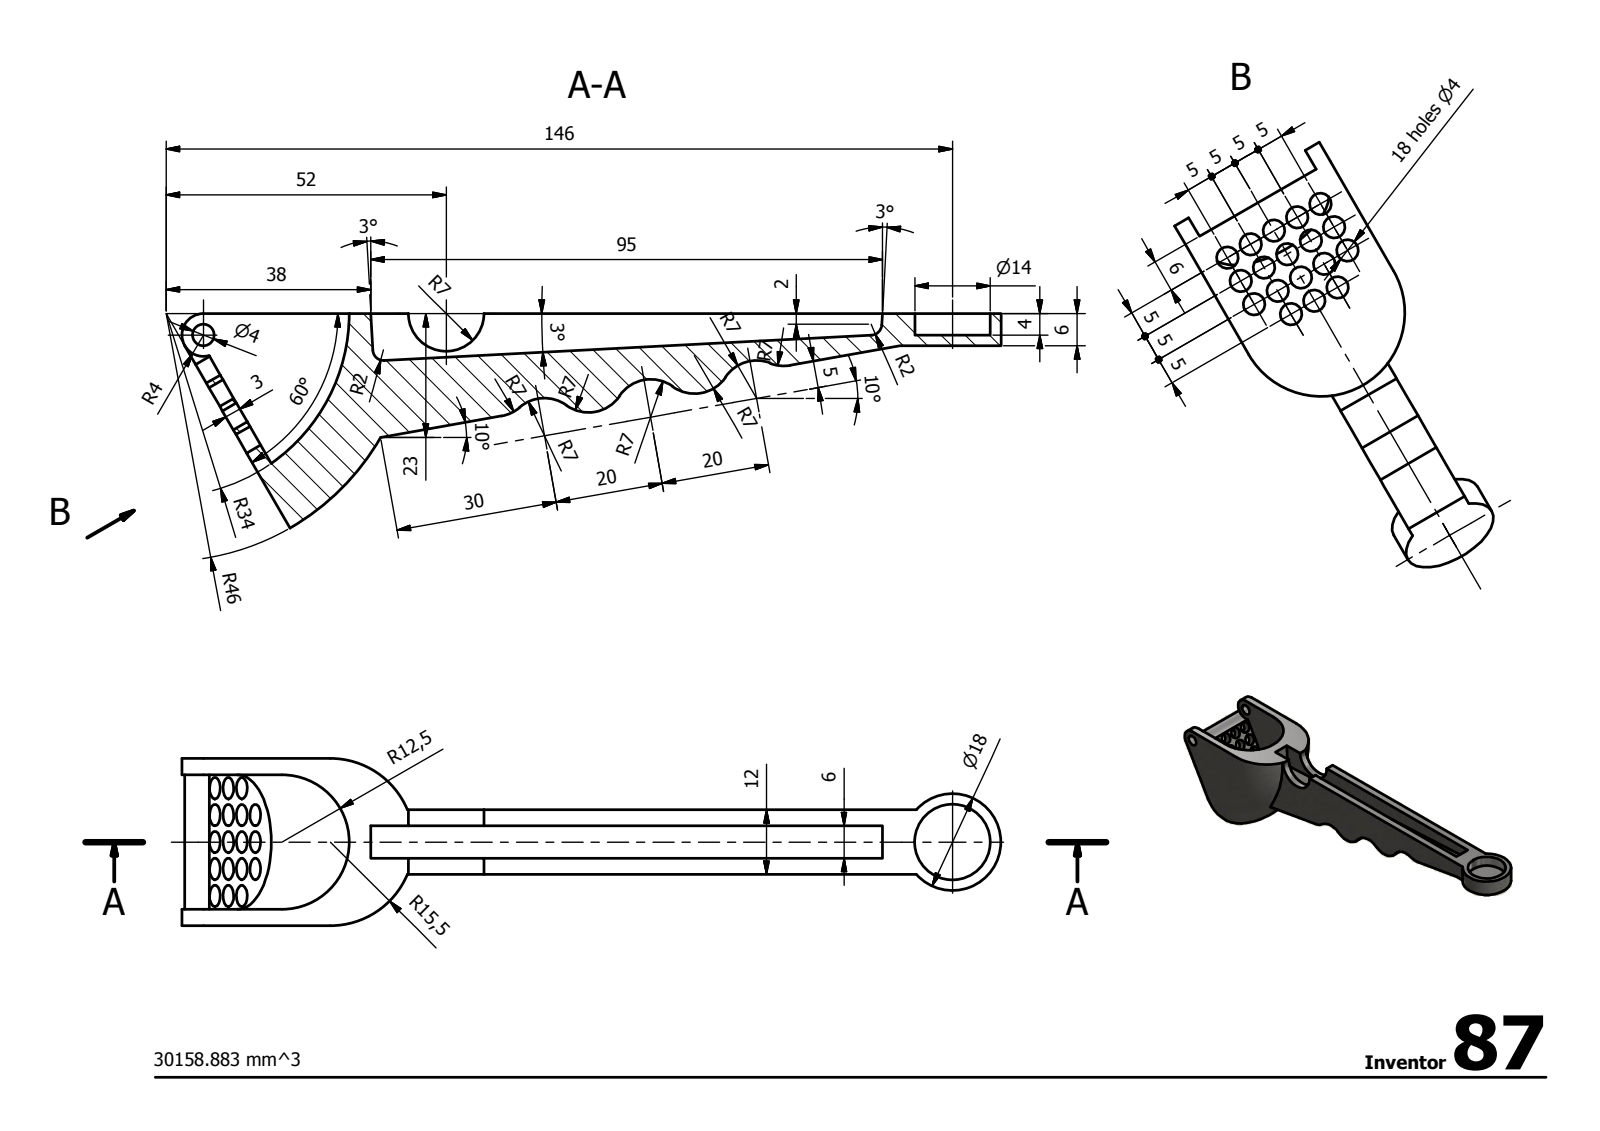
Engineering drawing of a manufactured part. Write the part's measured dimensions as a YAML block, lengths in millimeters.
step_written_by: "Autodesk Inventor 2014 (AUTOMOTIVE_DESIGN)"
units: millimeters
bodies: {solids: 1, faces: 57, planar: 19, cylindrical: 36, other: 2}
overall_size: [152.07, 39.84, 31]
volume: 30161
surface_area: 13748
round_holes:
  - {diameter: 4, count: 19}
  - {diameter: 14, count: 1}
partial_cylinders:
  - {radius: 7, count: 8}
  - {radius: 2, count: 2}
  - {radius: 4, count: 1}
  - {radius: 9, count: 1}
face_to_face_distances: [3, 9.5, 18.5, 12, 9, 12.5, 21.5, 6, 31, 28]
hole_center_spacings: [11.18, 5, 7.07, 10, 15.81, 14.14, 18.03, 15]
